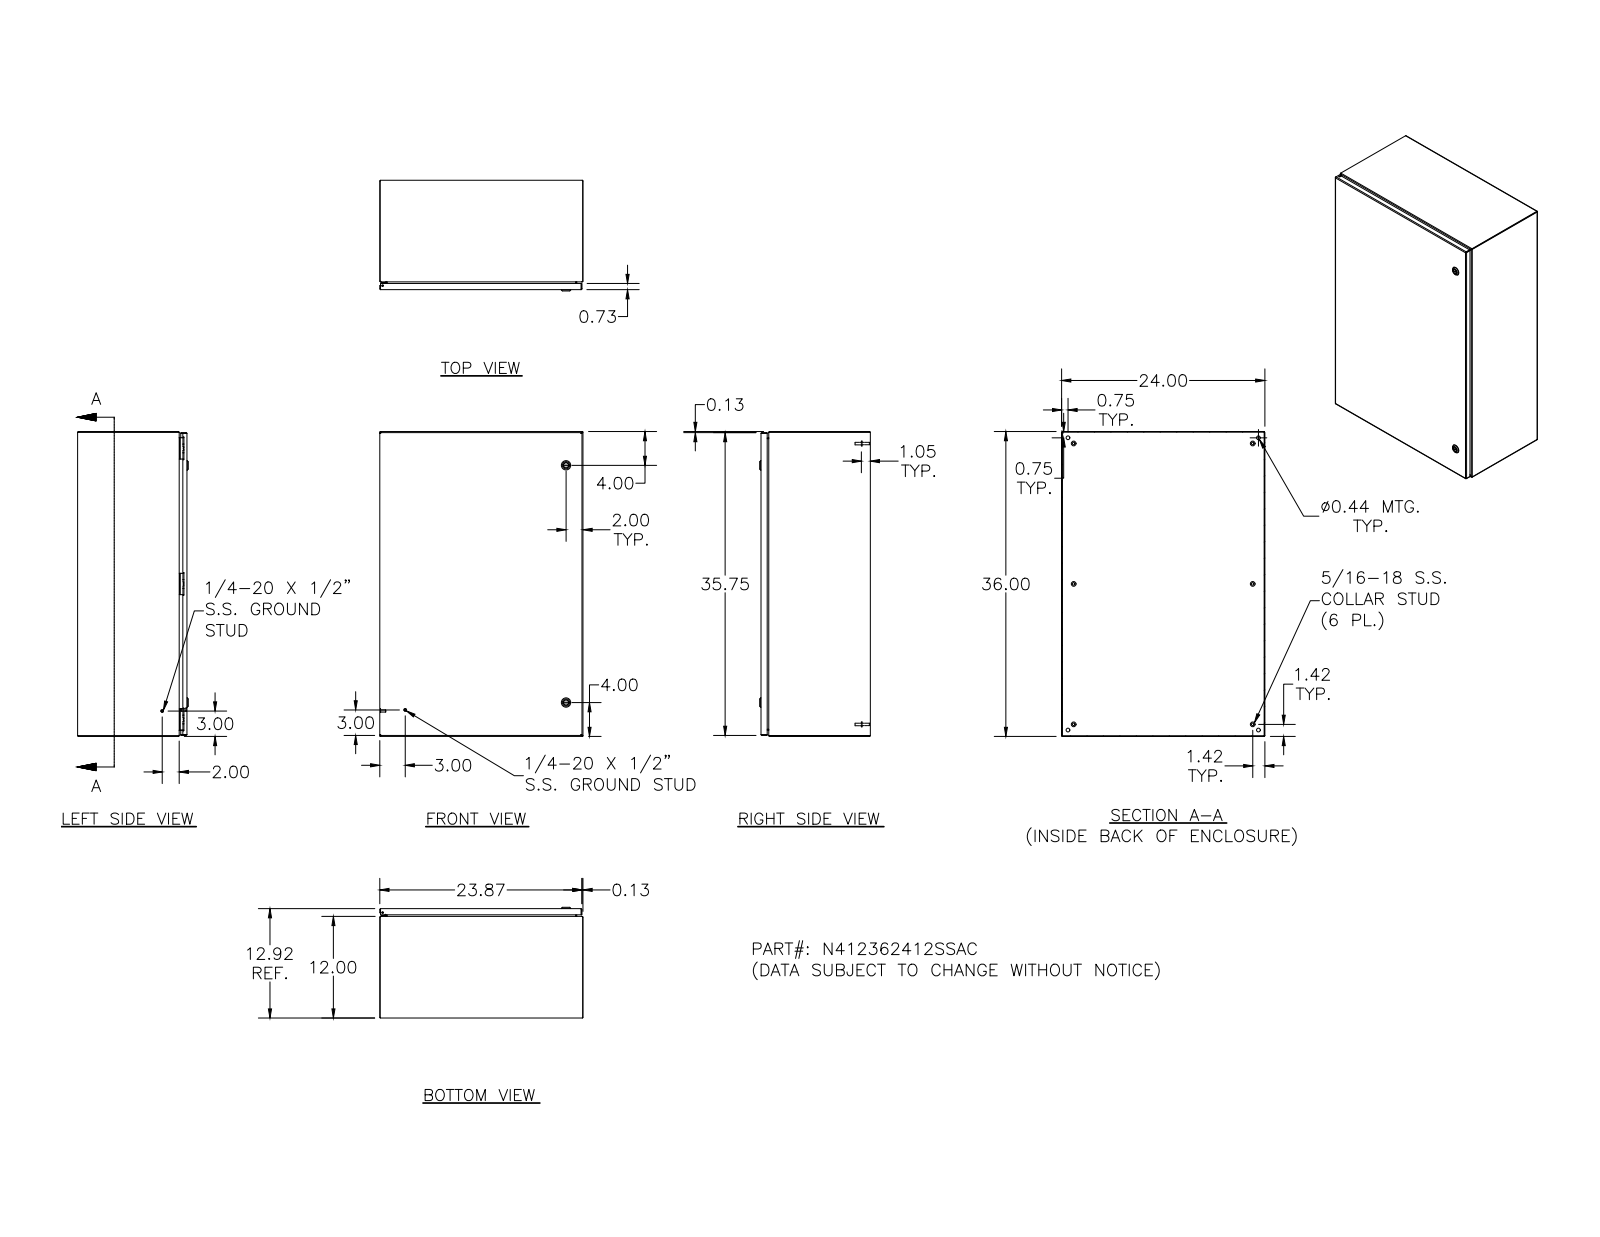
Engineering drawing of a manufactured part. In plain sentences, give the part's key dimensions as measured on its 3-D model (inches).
The part is named "N412362412SSAC; N412362412SSACBKP; 388151; N4123624SSACLID (+8 more)". Its 3-D file was written by "Autodesk Inventor 2011 (AUTOMOTIVE_DESIGN)". It is 53 solids with 2098 faces: 823 planar, 766 cylindrical and 509 other. Overall it measures 36 by 24 by 13.075 inches. Its volume is 253.3 cubic inches and its surface area 6 871 square inches. Round holes: 7 of diameter 0.188, 6 of diameter 0.093, 6 of diameter 0.152, 6 of diameter 0.167, 6 of diameter 0.172, 4 of diameter 0.437, 3 of diameter 0.156, 2 of diameter 0.197, 2 of diameter 0.315, 2 of diameter 0.394, 2 of diameter 0.402, 2 of diameter 0.634. Round bosses or shafts: 14 of diameter 0.25, 6 of diameter 0.563, 6 of diameter 0.36, 6 of diameter 0.32, 6 of diameter 0.3, 6 of diameter 0.275, 6 of diameter 0.256, 6 of diameter 0.164. Partial cylindrical surfaces (rounded edges, fillets, slot ends): 38 of radius 0.05, 26 of radius 0.016, 21 of radius 0.125, 18 of radius 0.031, 16 of radius 0.016, 16 of radius 0.09, 15 of radius 0.02, 12 of radius 0.032. The main face-to-face distances are 0.074, 12.843, 23.926, 12.769, 12.917, 35.926, 23.852, 24, 36, 35.852. The hole center spacings are 16.004, 32, 15.996, 0.017, 0.66, 15.992, 16, 16.008.
